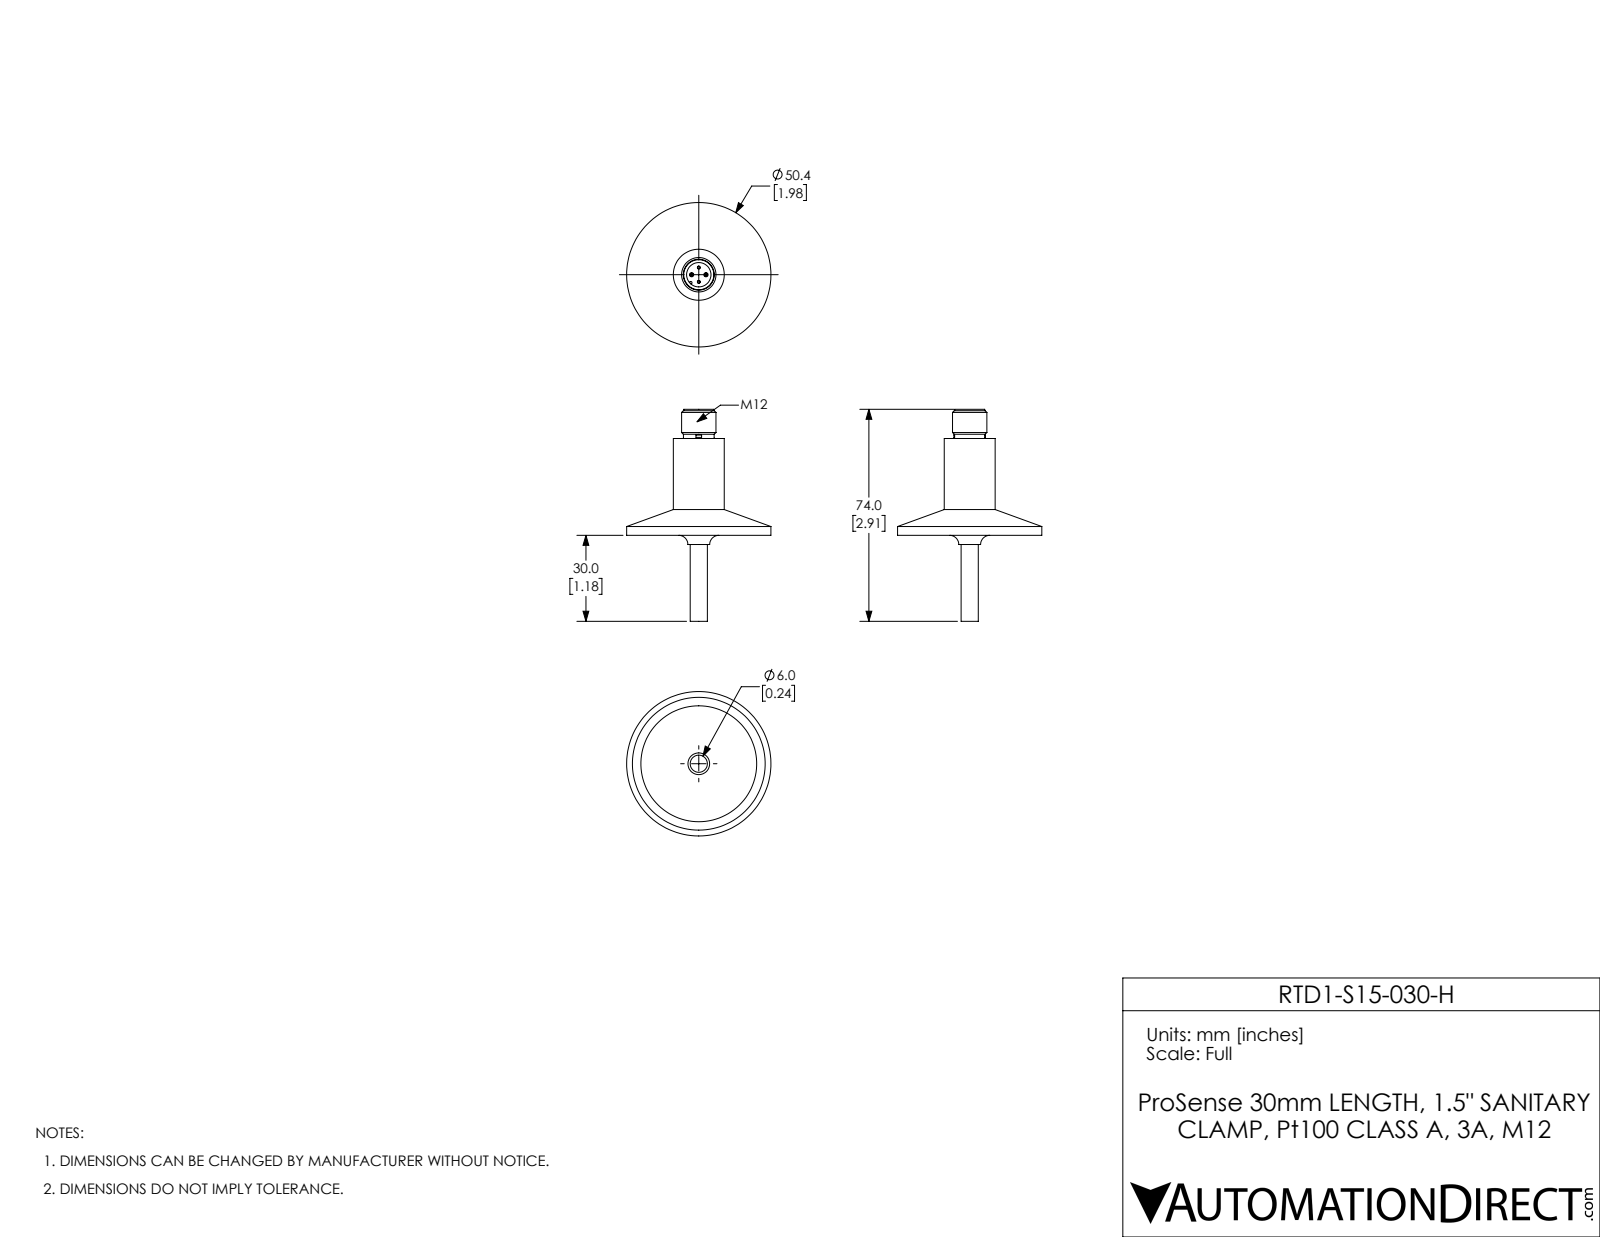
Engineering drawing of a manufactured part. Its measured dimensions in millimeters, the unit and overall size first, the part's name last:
Units: millimetres
Overall size (bounding box): 74 × 50.4 × 50.4
Round holes (diameter × count): ⌀8.5 ×1
Round bosses / shafts (diameter × count): ⌀1 ×4, ⌀50.4 ×1, ⌀17.8 ×1, ⌀12 ×1, ⌀10.7 ×1, ⌀10.5 ×1, ⌀6 ×1
Partial cylindrical surfaces — rounded edges, fillets, slot ends (radius × count): R0.4 ×1
Main face-to-face distances: 33.8, 35, 1.2, 44, 10.2, 9, 30, 63.8, 65, 74
Volume: 19 220 mm³ · Surface area: 7 452 mm²
Bodies: 1 solid, 79 faces (26 planar, 23 cylindrical, 30 other)
Part name (STEP PRODUCT): RTD1-S15-030-H
STEP written by: SolidWorks 2017 (AUTOMOTIVE_DESIGN)
